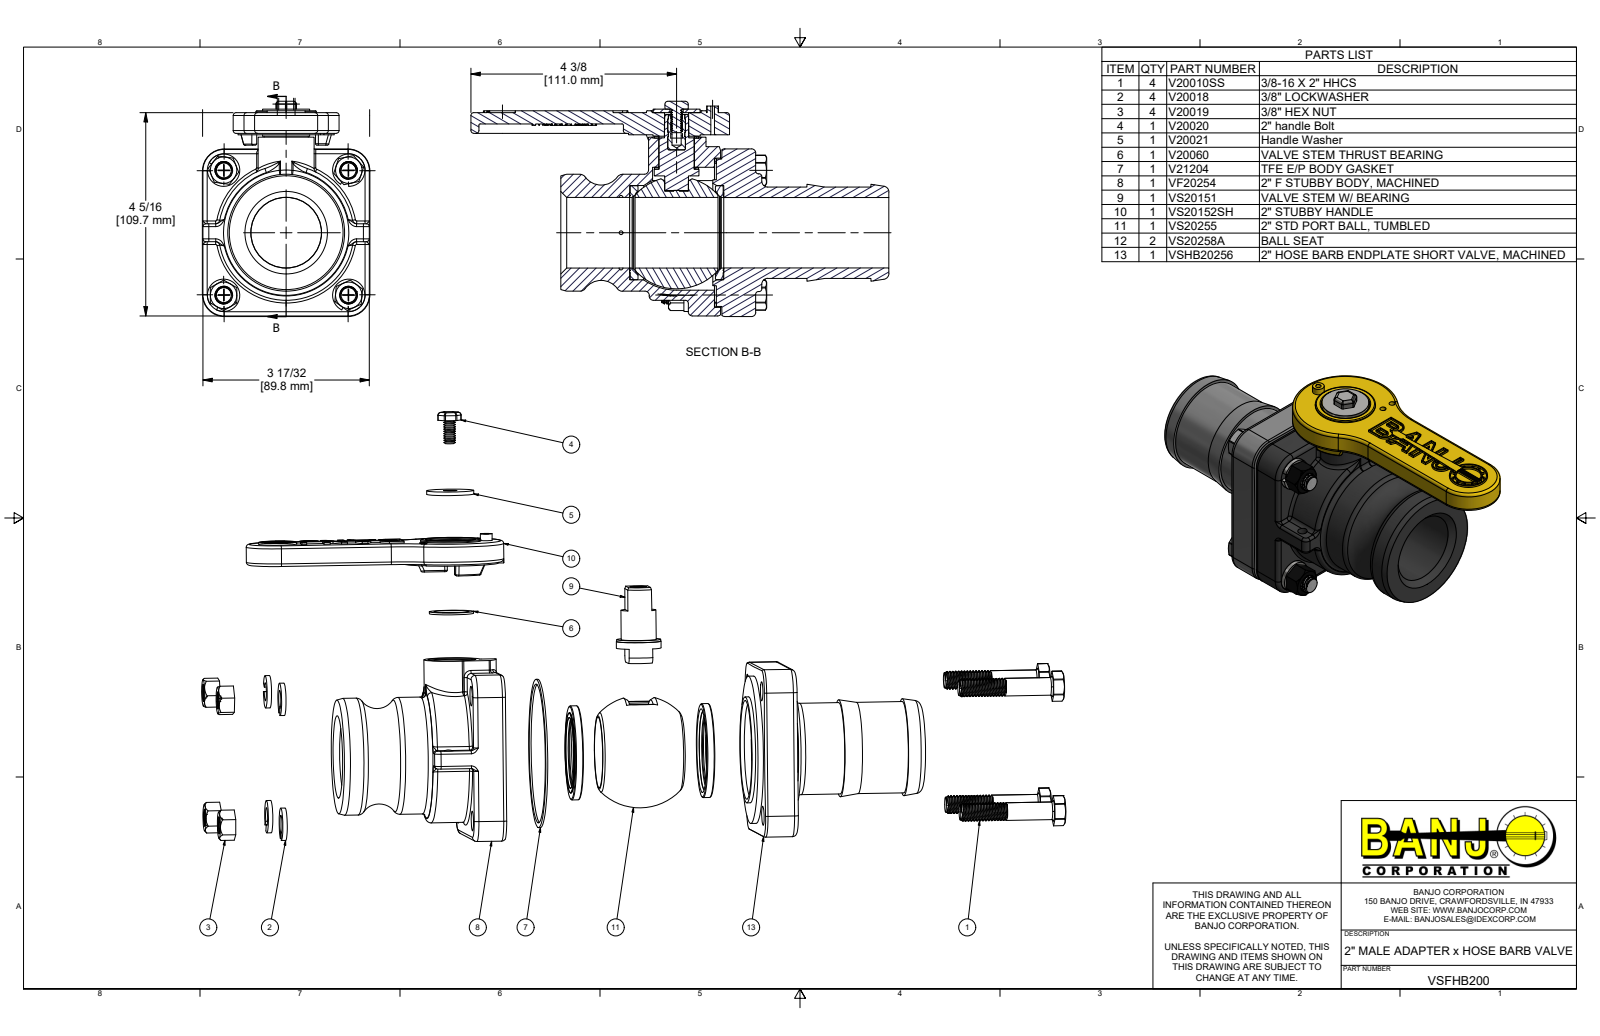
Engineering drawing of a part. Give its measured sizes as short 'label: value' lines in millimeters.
name: VSFHB200; VF20254; VXF20254; VSHB20256 (+8 more)
written by: Autodesk Inventor 2017 (AUTOMOTIVE_DESIGN)
unit: mm
bodies: 25 solids, 2394 faces (876 planar, 604 cylindrical, 914 other)
size: 225.59 × 116.1 × 90.42
volume: 514 826 mm³; area: 158 139 mm²
holes: 8× ⌀10.31, 5× ⌀9.52, 4× ⌀7.81, 4× ⌀9.78, 2× ⌀2.03, 2× ⌀3.3, 2× ⌀5.08, 1× ⌀3, 1× ⌀4.98, 1× ⌀7.14, 1× ⌀8.92, 1× ⌀13.83
bosses: 60× ⌀8.24, 4× ⌀17.46, 4× ⌀9.52, 1× ⌀80.01, 1× ⌀79.5, 1× ⌀63.5, 1× ⌀63.04, 1× ⌀57.15
rounds: 26× R1.52, 21× R2.29, 15× R0.76, 8× R3.17, 8× R4.12, 4× R8.12, 4× R11.89, 4× R11.91
face distances: 90.42, 21.21, 36.36, 15.15, 1.02, 6.86, 2.31, 18.9, 17.46, 12.7
hole spacings: 67.39, 47.56, 47.74, 67.26, 67.52, 95.3, 40.46, 46.12
